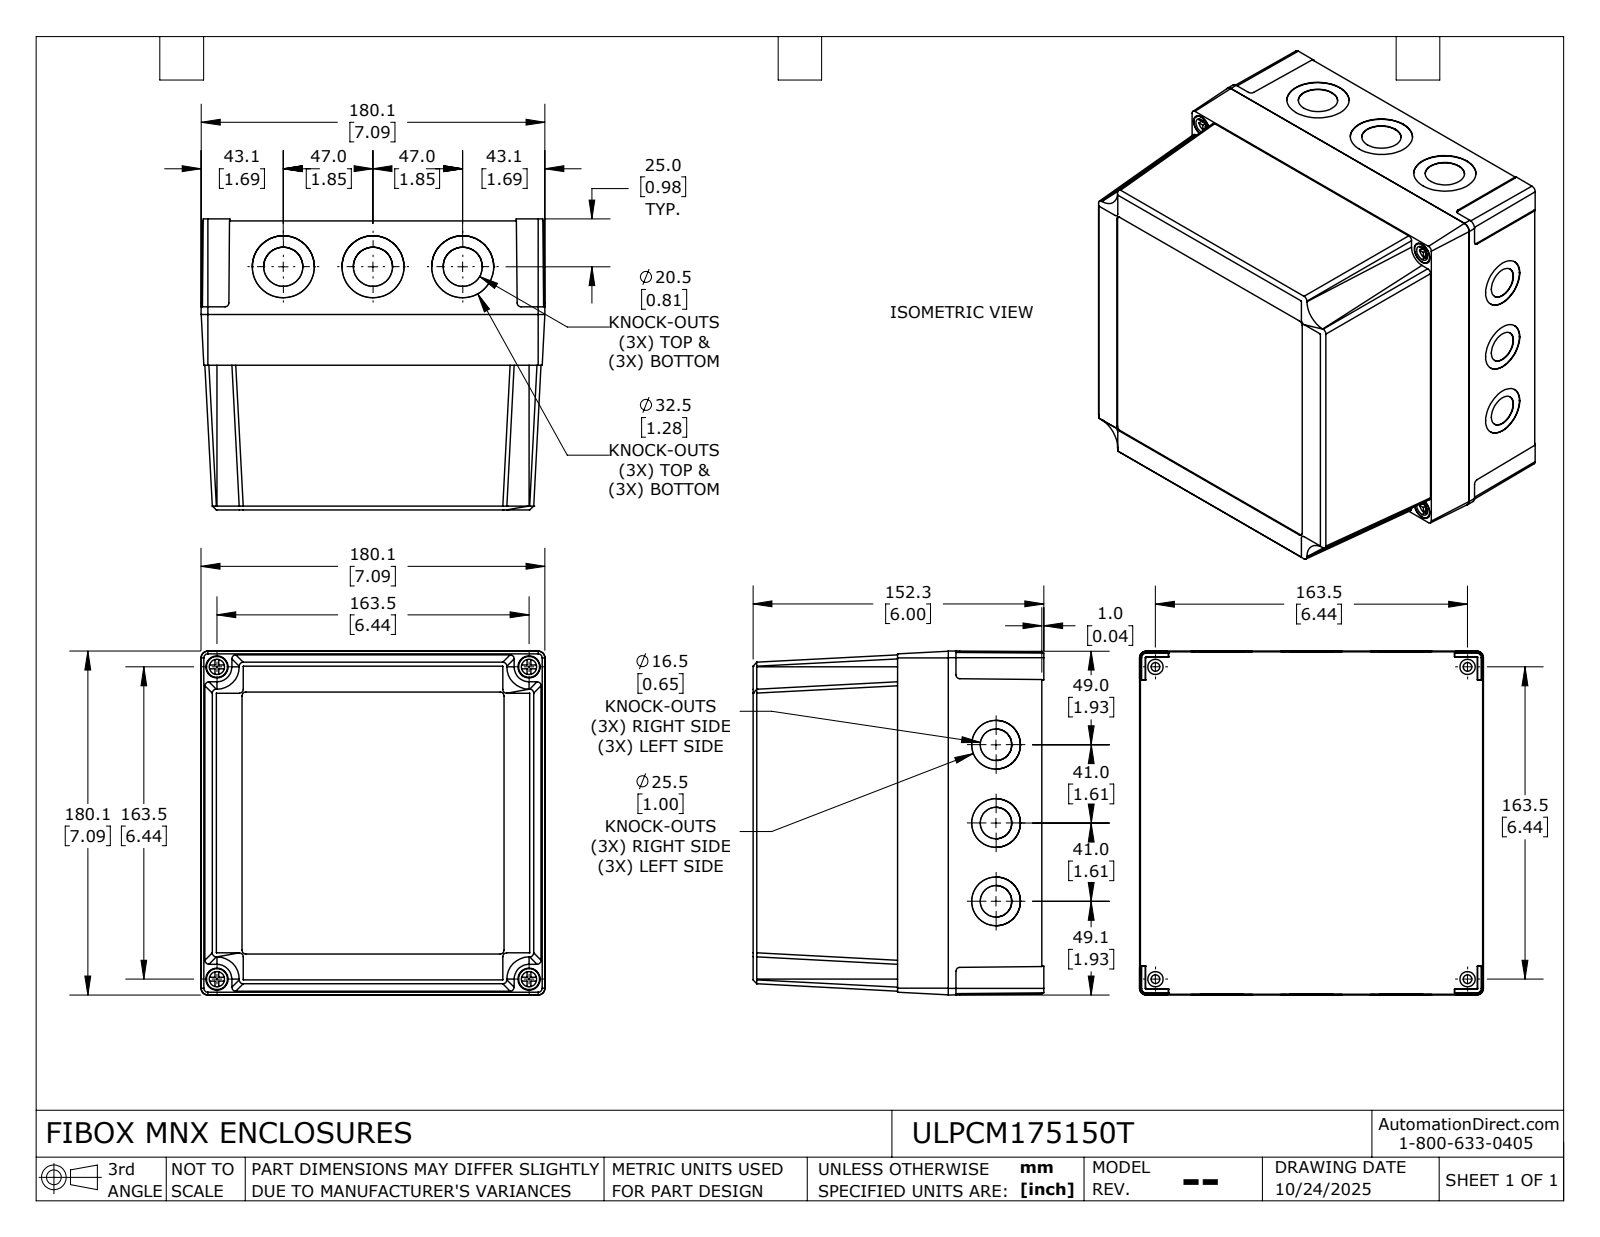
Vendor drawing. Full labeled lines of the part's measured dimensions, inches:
Part name (STEP PRODUCT): ULPCM175150T_Default
STEP written by: SolidWorks 2024 (CONFIG_CONTROL_DESIGN)
Units: inches
Bodies: 6 solids, 633 faces (355 planar, 232 cylindrical, 46 other)
Overall size (bounding box): 7.091 × 7.091 × 5.996
Volume: 28.98 in³ · Surface area: 529 in²
Round holes (diameter × count): ⌀0.126 ×12, ⌀0.157 ×12, ⌀0.65 ×6, ⌀0.807 ×6, ⌀1.004 ×6, ⌀1.28 ×6, ⌀0.177 ×4, ⌀0.315 ×4, ⌀0.457 ×4
Round bosses / shafts (diameter × count): ⌀0.315 ×12, ⌀0.098 ×8, ⌀0.433 ×4, ⌀0.283 ×4
Partial cylindrical surfaces — rounded edges, fillets, slot ends (radius × count): R0.079 ×8, R0.083 ×8, R0.112 ×6, R0.042 ×4, R0.197 ×4, R0.046 ×2
Main face-to-face distances: 0.079, 0.118, 5.858, 5.74, 0.165, 5.819, 5.937, 0.101, 0.022, 0.098
Hole centre spacings: 1.333, 1.969, 2.866, 3.252, 4.79, 5.207, 5.469, 5.853
